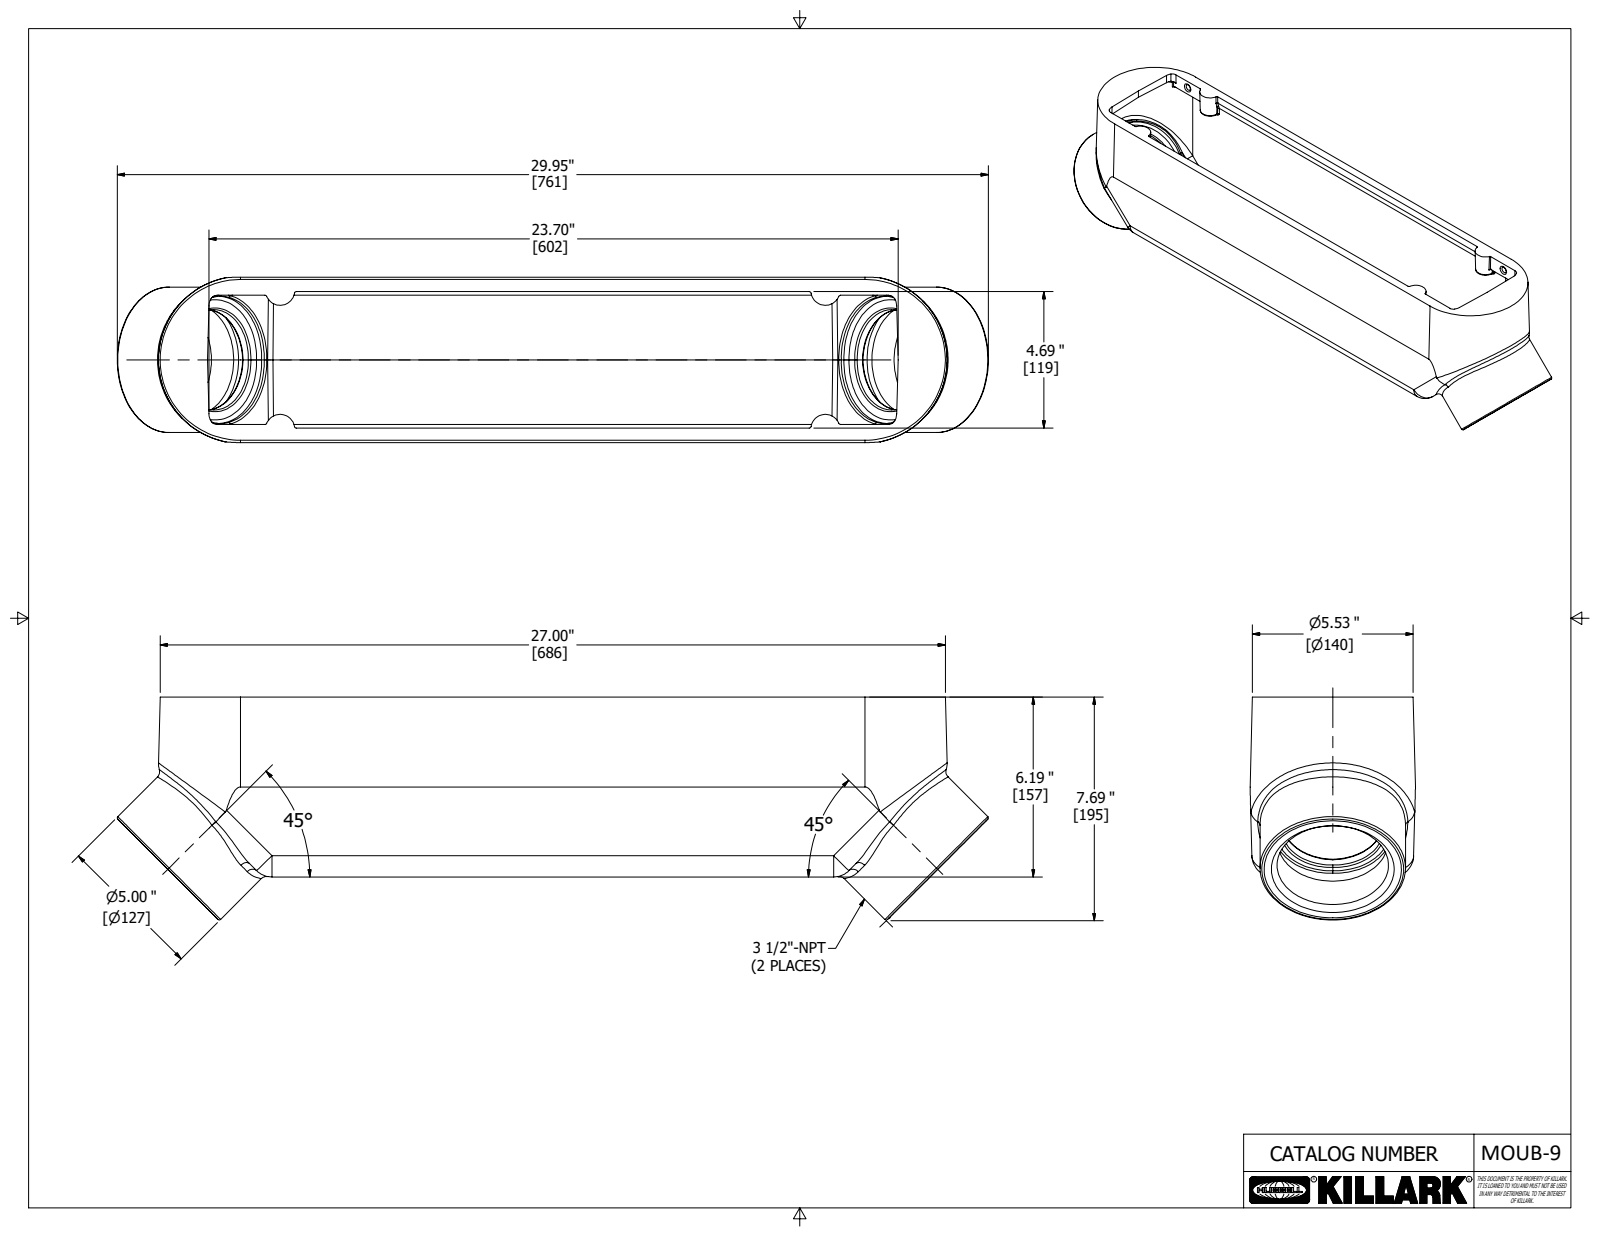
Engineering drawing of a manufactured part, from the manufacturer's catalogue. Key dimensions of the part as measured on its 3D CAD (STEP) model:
Part name (STEP PRODUCT): 21355
STEP written by: Autodesk Inventor 2020 (AUTOMOTIVE_DESIGN)
Units: inches
Bodies: 1 solid, 680 faces (282 planar, 60 cylindrical, 338 other)
Overall size (bounding box): 29.955 × 7.665 × 5.688
Volume: 195.9 in³ · Surface area: 1 033 in²
Round holes (diameter × count): ⌀3.448 ×2, ⌀4.011 ×2, ⌀4.375 ×2
Round bosses / shafts (diameter × count): ⌀5 ×2
Partial cylindrical surfaces — rounded edges, fillets, slot ends (radius × count): R0.062 ×18, R0.25 ×14, R0.75 ×8, R0.125 ×4, R0.5 ×4, R2.469 ×2
Main face-to-face distances: 5.688, 4.938, 6.187, 0.031, 6.156, 0.125, 4.813, 4.906, 0.031, 0.094
